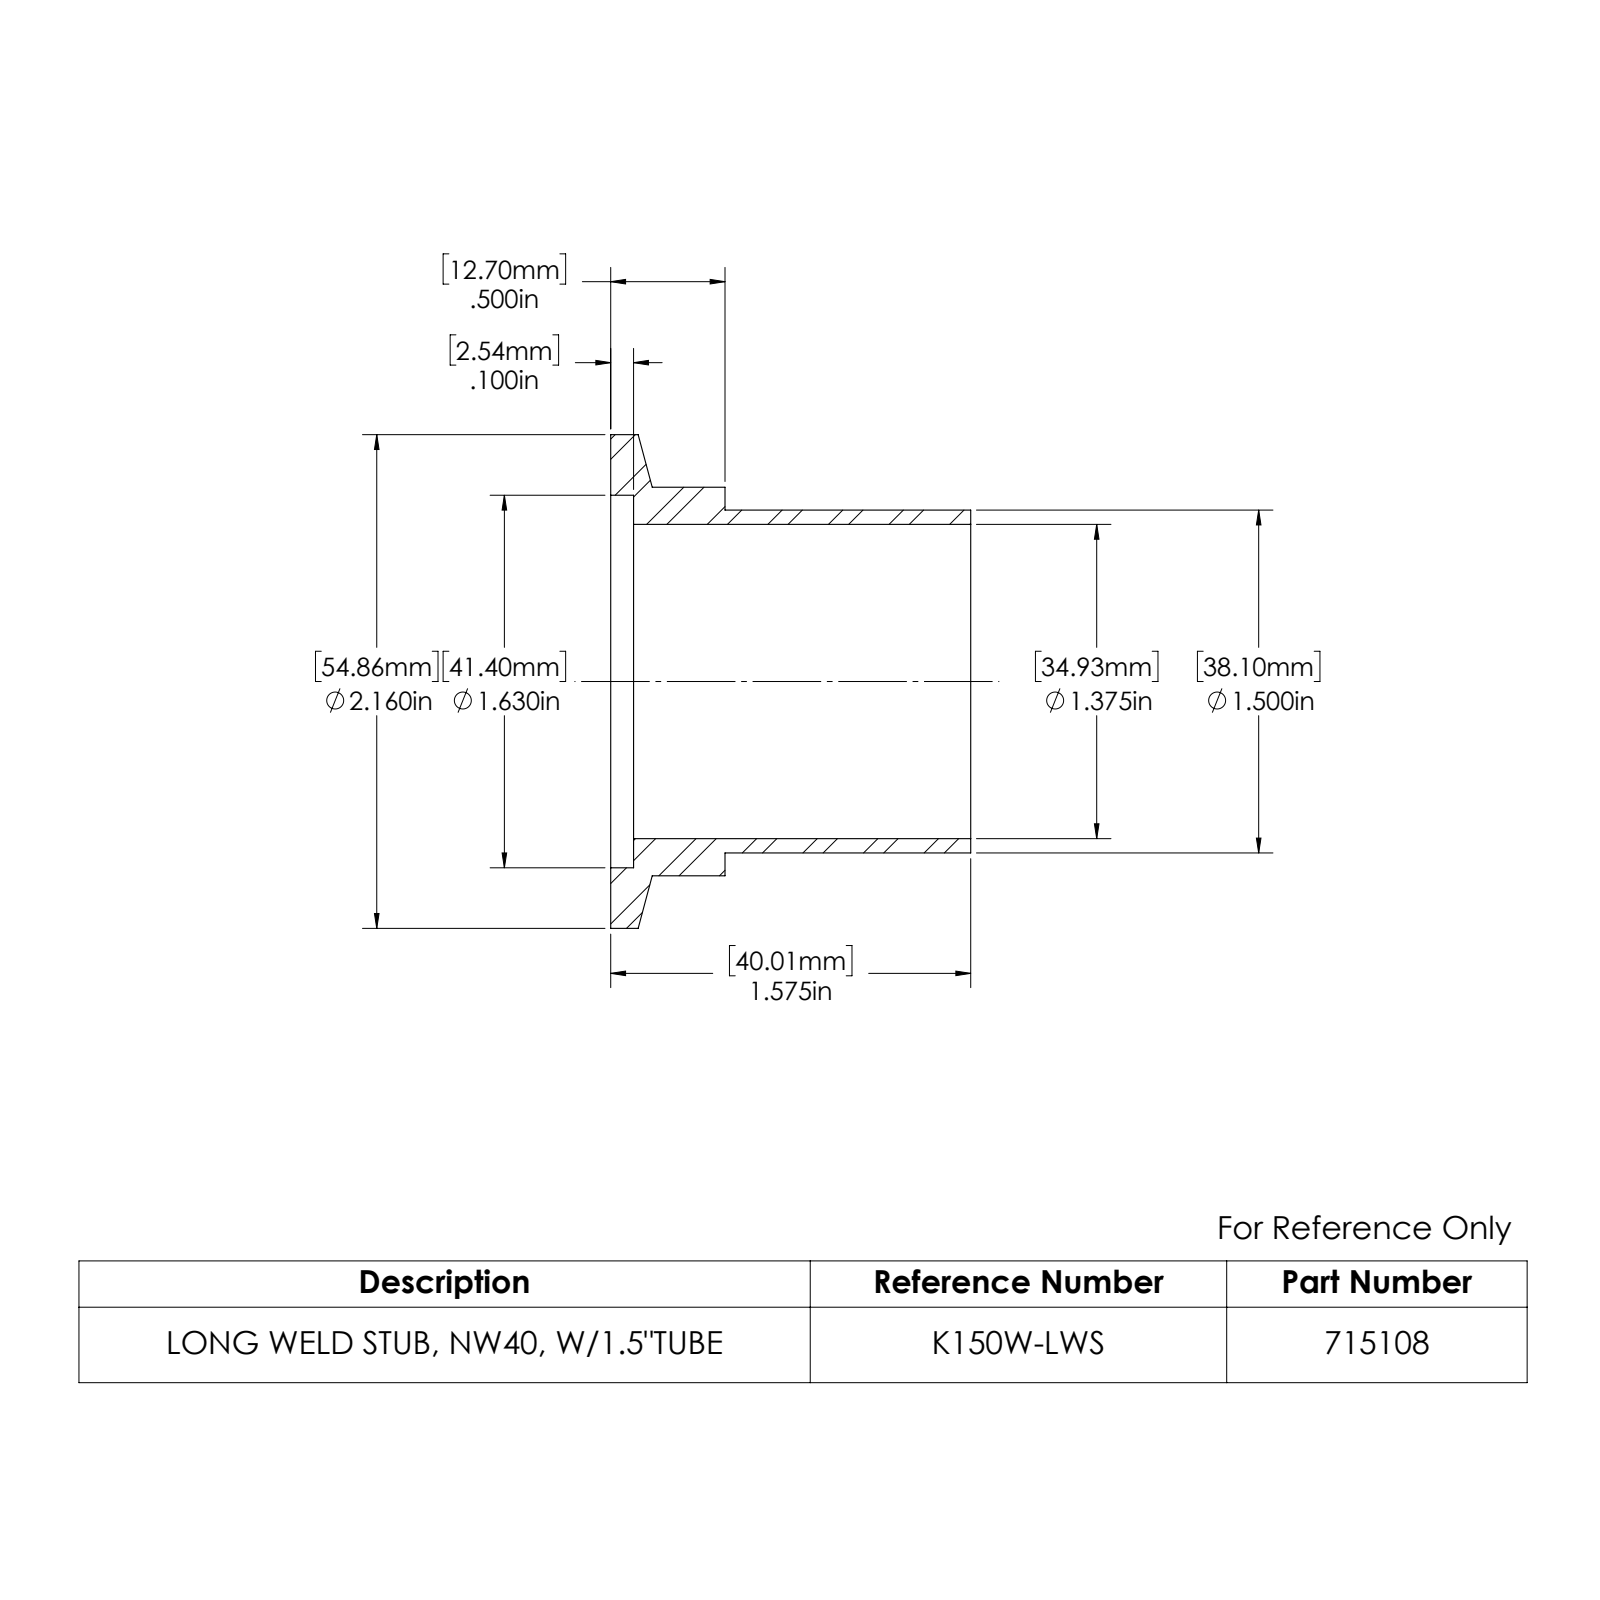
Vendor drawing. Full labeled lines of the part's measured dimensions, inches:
Part name (STEP PRODUCT): 715108
STEP written by: SolidWorks 2022 (AUTOMOTIVE_DESIGN)
Units: inches
Bodies: 1 solid, 16 faces (4 planar, 10 cylindrical, 2 other)
Overall size (bounding box): 2.16 × 2.16 × 1.575
Volume: 0.844 in³ · Surface area: 18.87 in²
Round holes (diameter × count): ⌀1.375 ×1, ⌀1.63 ×1
Round bosses / shafts (diameter × count): ⌀2.16 ×1, ⌀1.7 ×1, ⌀1.5 ×1
Main face-to-face distances: 0.1, 0.4, 0.5, 1.075, 1.475, 1.575
